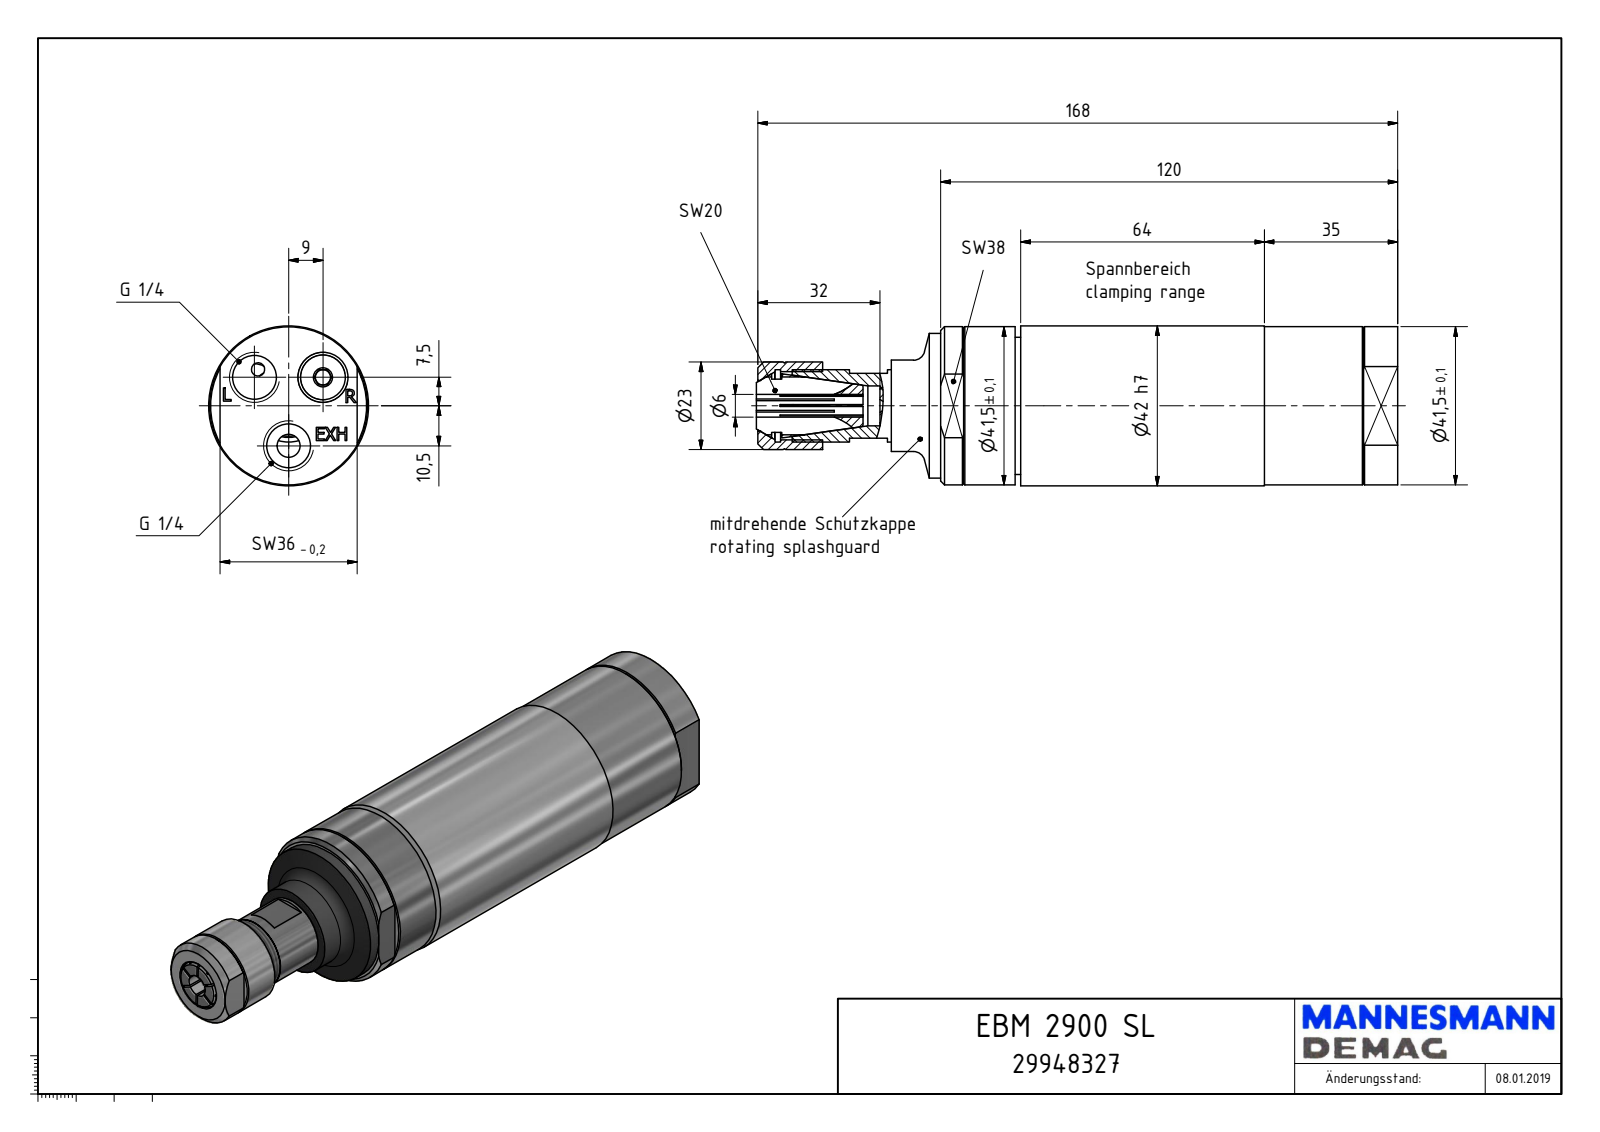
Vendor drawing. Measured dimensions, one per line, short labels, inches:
name: EBM 2900 SL_29948327
written by: Autodesk Inventor 2018 (AUTOMOTIVE_DESIGN)
unit: in
bodies: 1 solid, 289 faces (169 planar, 51 cylindrical, 69 other)
size: 6.631 × 1.654 × 1.654
volume: 10.81 in³; area: 44.75 in²
holes: 3× ⌀0.451, 2× ⌀0.236, 1× ⌀0.157, 1× ⌀0.52, 1× ⌀0.706, 1× ⌀0.748, 1× ⌀1.496
bosses: 1× ⌀1.654, 1× ⌀1.634, 1× ⌀1.496, 1× ⌀1.493, 1× ⌀1.417, 1× ⌀0.945, 1× ⌀0.906, 1× ⌀0.747
rounds: 6× R0.712, 6× R1.328
face distances: 0.02, 3.898, 0.059, 3.957, 0.039, 0.669, 0.354, 1.102, 1.457, 3.273
hole spacings: 0.461, 0.792, 0.413, 0.709
